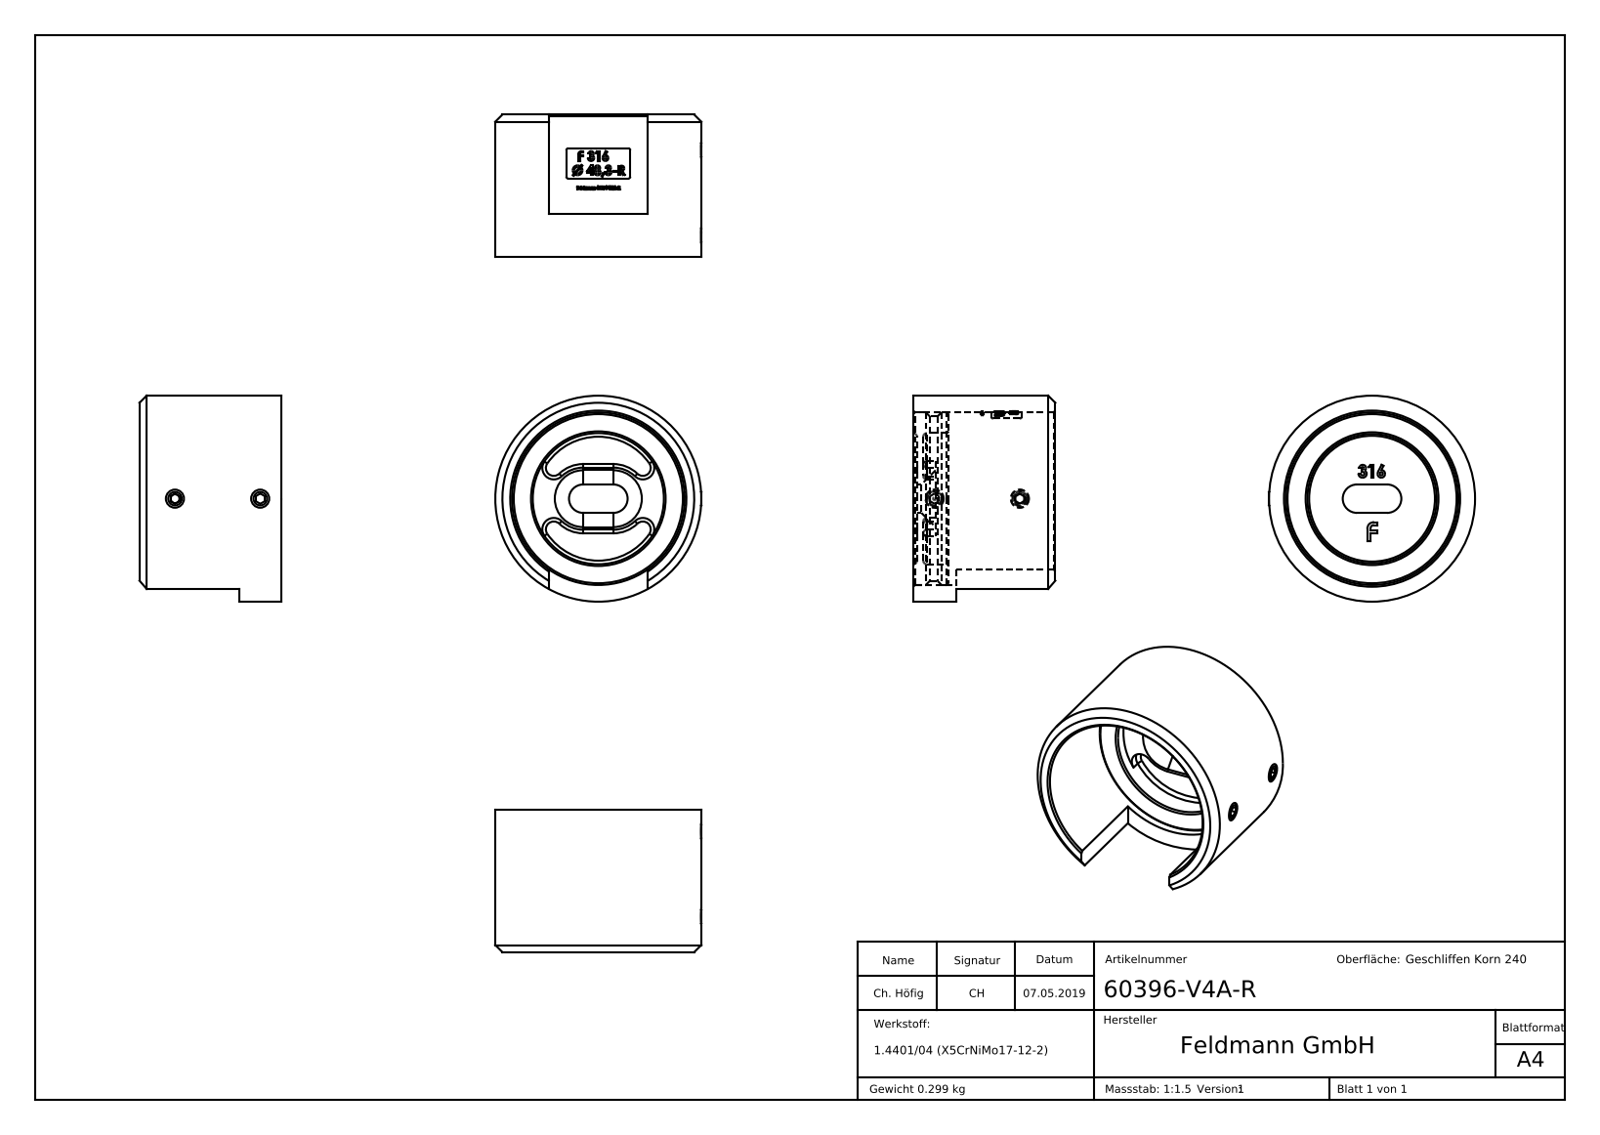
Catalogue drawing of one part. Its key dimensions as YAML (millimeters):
part_name: "60396-V4A-R; 6039X-240-X Teil2_60396-V4A-X Teil2; DIN913_DIN 913 M5x5; DIN914_DIN 914 M5x6 (+1 more)"
step_written_by: "SolidWorks 2015 (CONFIG_CONTROL_DESIGN)"
units: millimeters
bodies: {solids: 4, faces: 585, planar: 253, cylindrical: 87, other: 245}
overall_size: [58, 58, 40]
volume: 37345
surface_area: 19798
round_holes:
  - {diameter: 4.2, count: 2}
  - {diameter: 36.9, count: 1}
  - {diameter: 48.6, count: 1}
round_bosses_or_shafts:
  - {diameter: 5, count: 2}
  - {diameter: 58, count: 1}
  - {diameter: 46.34, count: 1}
partial_cylinders:
  - {radius: 0.5, count: 4}
  - {radius: 3.22, count: 4}
  - {radius: 1, count: 2}
  - {radius: 4, count: 2}
  - {radius: 8.75, count: 2}
  - {radius: 24.4, count: 1}
  - {radius: 24.5, count: 1}
face_to_face_distances: [1, 10, 9, 7.2, 2.8, 1.8, 40, 39, 37.2, 30]
hole_center_spacings: [24]
